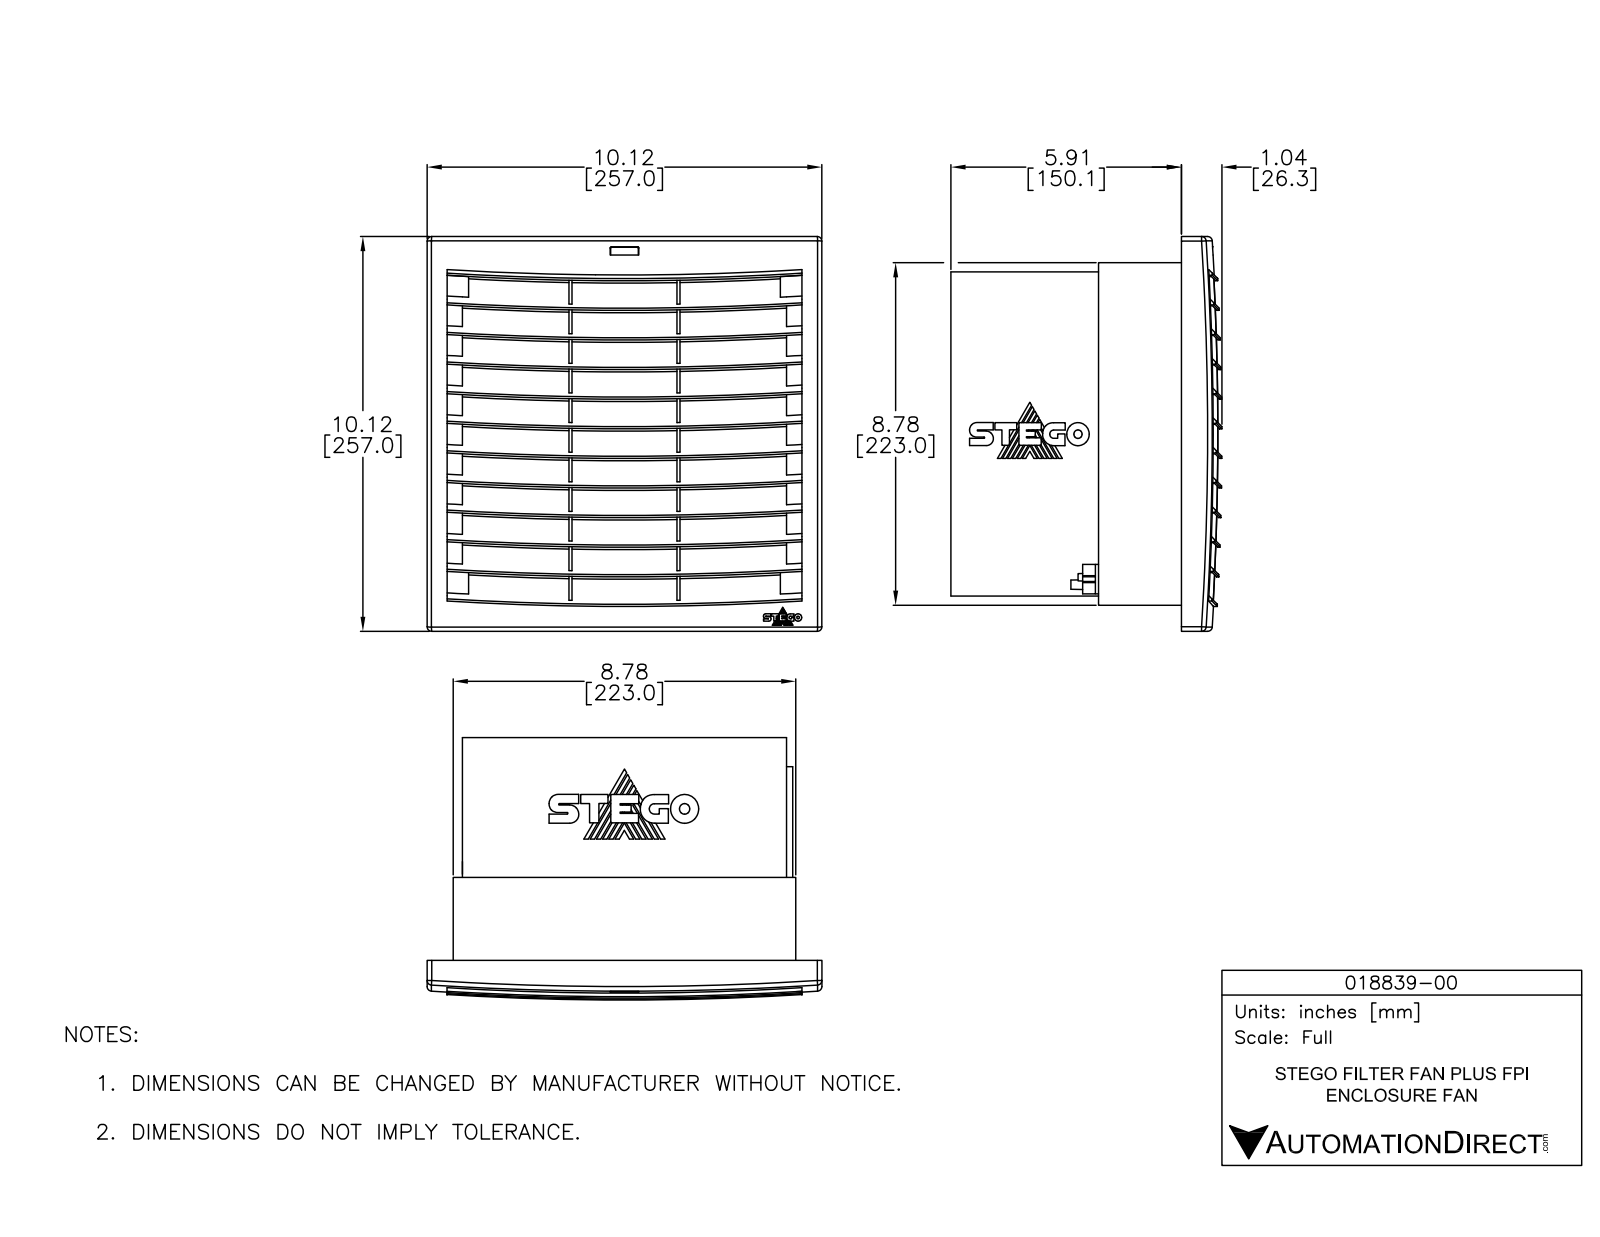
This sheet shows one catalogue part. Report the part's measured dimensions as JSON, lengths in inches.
{"part_name": "018839-00", "step_written_by": "SolidWorks 2018 (AUTOMOTIVE_DESIGN)", "units": "inches", "bodies": {"solids": 1, "faces": 833, "planar": 487, "cylindrical": 346, "other": 0}, "overall_size": [10.118, 10.118, 6.811], "volume_in3": 159.1, "surface_area_in2": 1062, "round_holes": [[2.268, 1], [3.018, 1], [3.769, 1], [4.487, 1], [4.52, 1], [5.27, 1], [5.42, 1], [6.021, 1], [6.353, 1], [6.929, 1], [7.463, 1]], "round_bosses_or_shafts": [[8.64, 1], [8.228, 1], [8.146, 1], [6.707, 1], [6.336, 1], [5.774, 1], [5.585, 1], [4.841, 1]], "partial_cylinders_radius": [[42.577, 21], [3.361, 5], [0.197, 4], [0.26, 4], [0.933, 1], [1.311, 1], [1.488, 1], [1.777, 1]], "face_to_face_distances": [0.059, 0.536, 0.242, 0.726, 0.484, 2.145, 2.681, 1.609, 0.22, 8.56]}
